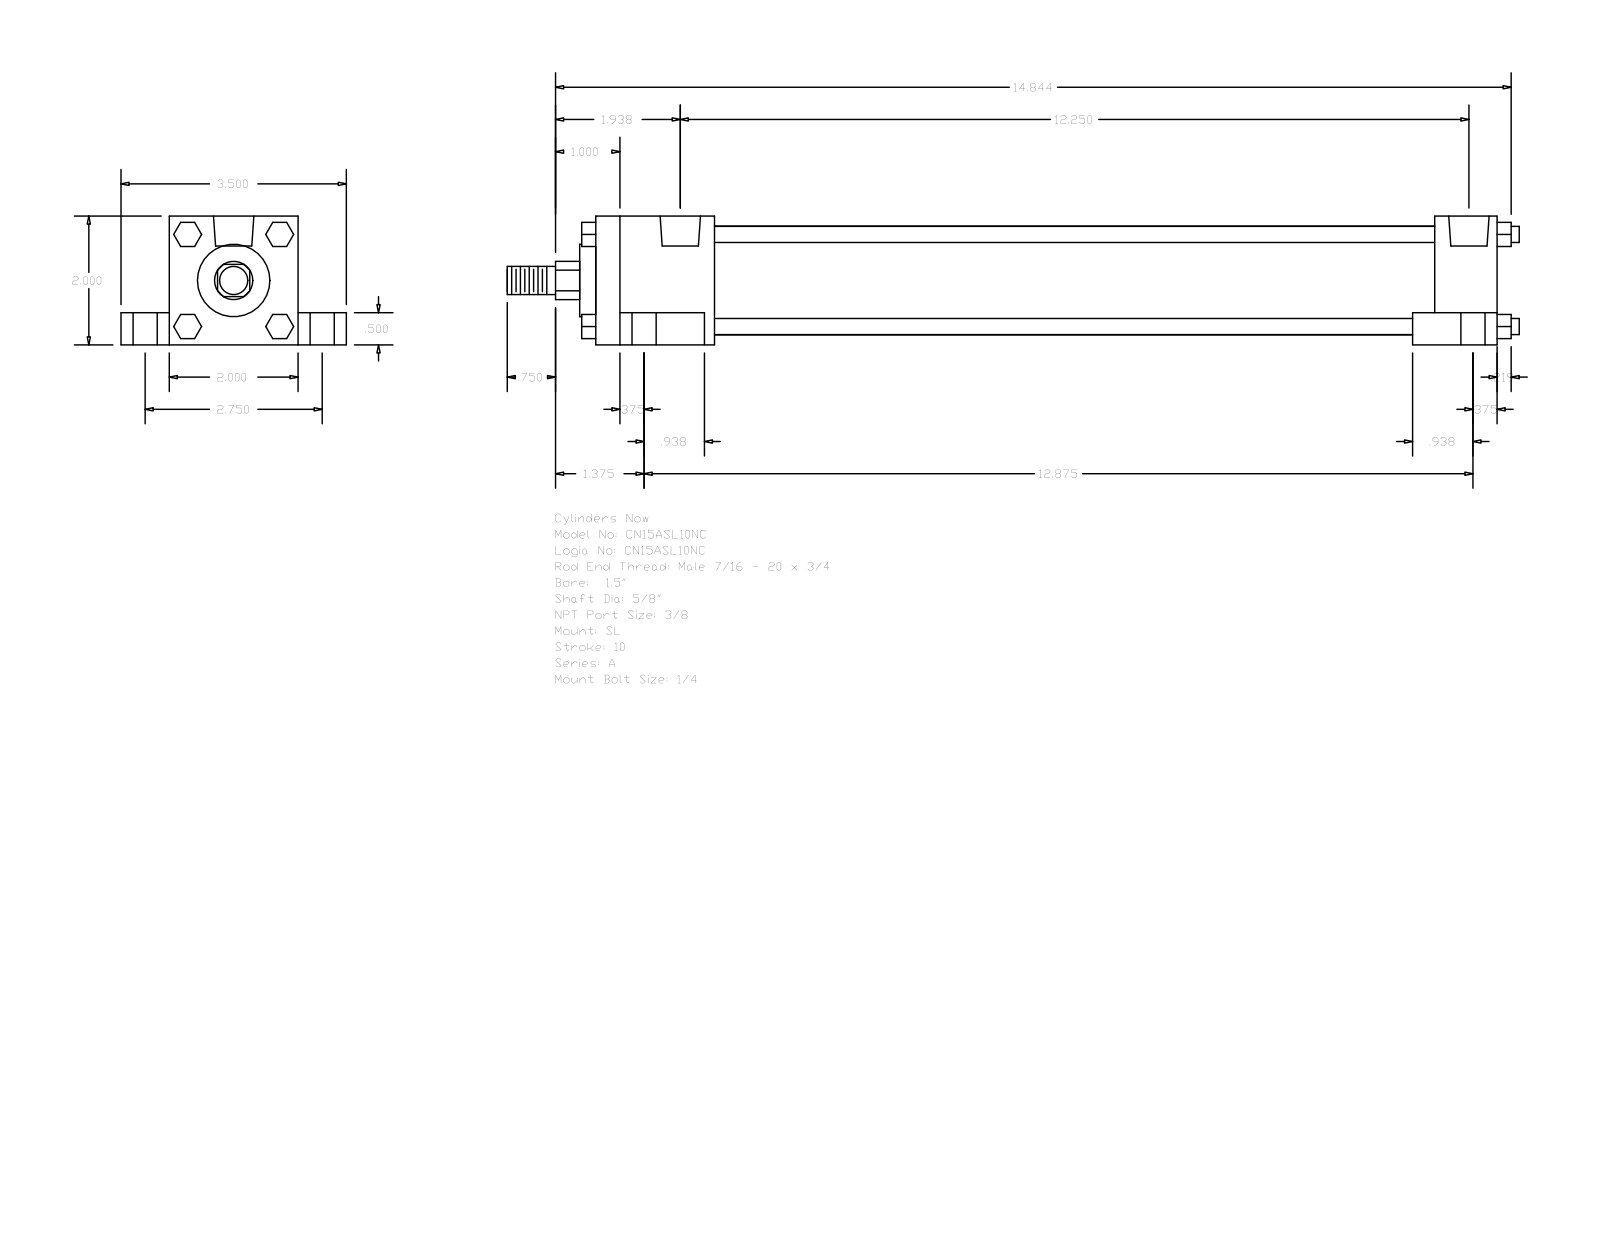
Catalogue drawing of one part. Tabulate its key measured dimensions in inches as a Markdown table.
| quantity | value |
| --- | --- |
| part name | A_SL__0150_0.625 |
| STEP written by | GSSL Pune (CONFIG_CONTROL_DESIGN) |
| units | inches |
| bodies | 0 solids, 148 faces (112 planar, 36 cylindrical, 0 other) |
| overall size | 15.719 × 3.5 × 2 |
| round holes (diameter × count) | 0.219 × 4, 0.375 × 4, 0.625 × 4, 0.627 × 2 |
| round bosses / shafts (diameter × count) | 0.25 × 4, 1.69 × 1, 1.125 × 1, 0.625 × 1, 0.437 × 1 |
| partial cylindrical surfaces (radius × count) | 0.297 × 1 |
| main face-to-face distances | 2, 0.75, 1.5, 0.5, 2.75, 14, 0.375, 1.313, 13.031, 0.969 |
| hole center spacings | 0.156, 1.376, 1.392, 1.485, 1.552, 2.75, 11.937, 12.094 |
